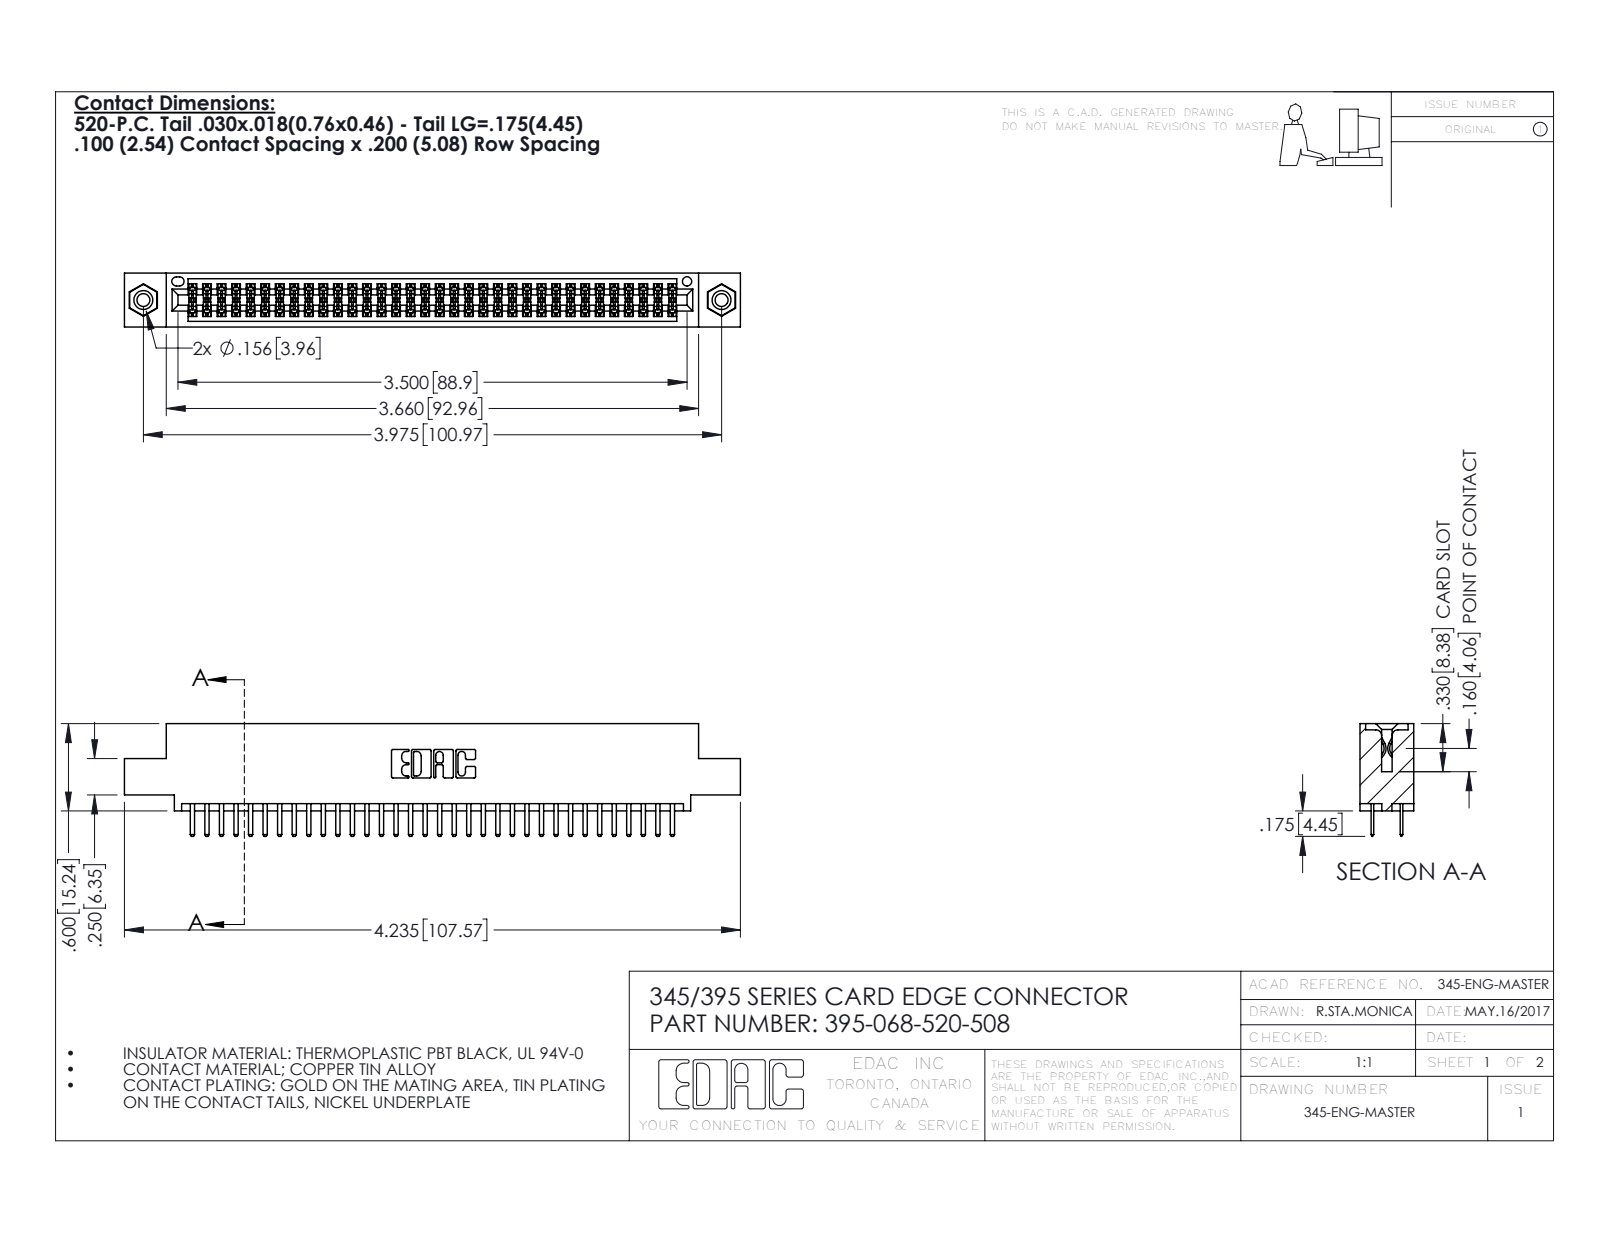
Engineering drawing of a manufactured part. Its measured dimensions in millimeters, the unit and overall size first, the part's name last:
Units: millimetres
Overall size (bounding box): 107.6 × 19.7 × 9.4
Round holes (diameter × count): ⌀2.3 ×2, ⌀3.2 ×2, ⌀4 ×2, ⌀1.6 ×1
Round bosses / shafts (diameter × count): ⌀3.9 ×2
Partial cylindrical surfaces — rounded edges, fillets, slot ends (radius × count): R0.2 ×102, R0.3 ×72, R0.3 ×22, R0.2 ×6, R0.8 ×6, R0.7 ×3, R0.4 ×2, R0.5 ×2
Main face-to-face distances: 1.8, 7.6, 5.1, 9.4, 2.5, 6.9, 0.6, 5.7, 0.6, 1.8
Hole centre spacings: 6.9, 95, 101
Volume: 10 300 mm³ · Surface area: 15 060 mm²
Bodies: 71 solids, 3862 faces (2496 planar, 1350 cylindrical, 16 other)
Part name (STEP PRODUCT): 345 Part_0.110 Offset - 0.156 Dia-TI; 345-292-001_345-293-120; 395-068-520-508; 345-250-001_345-250-003-102
STEP written by: SolidWorks 2016 (CONFIG_CONTROL_DESIGN)
